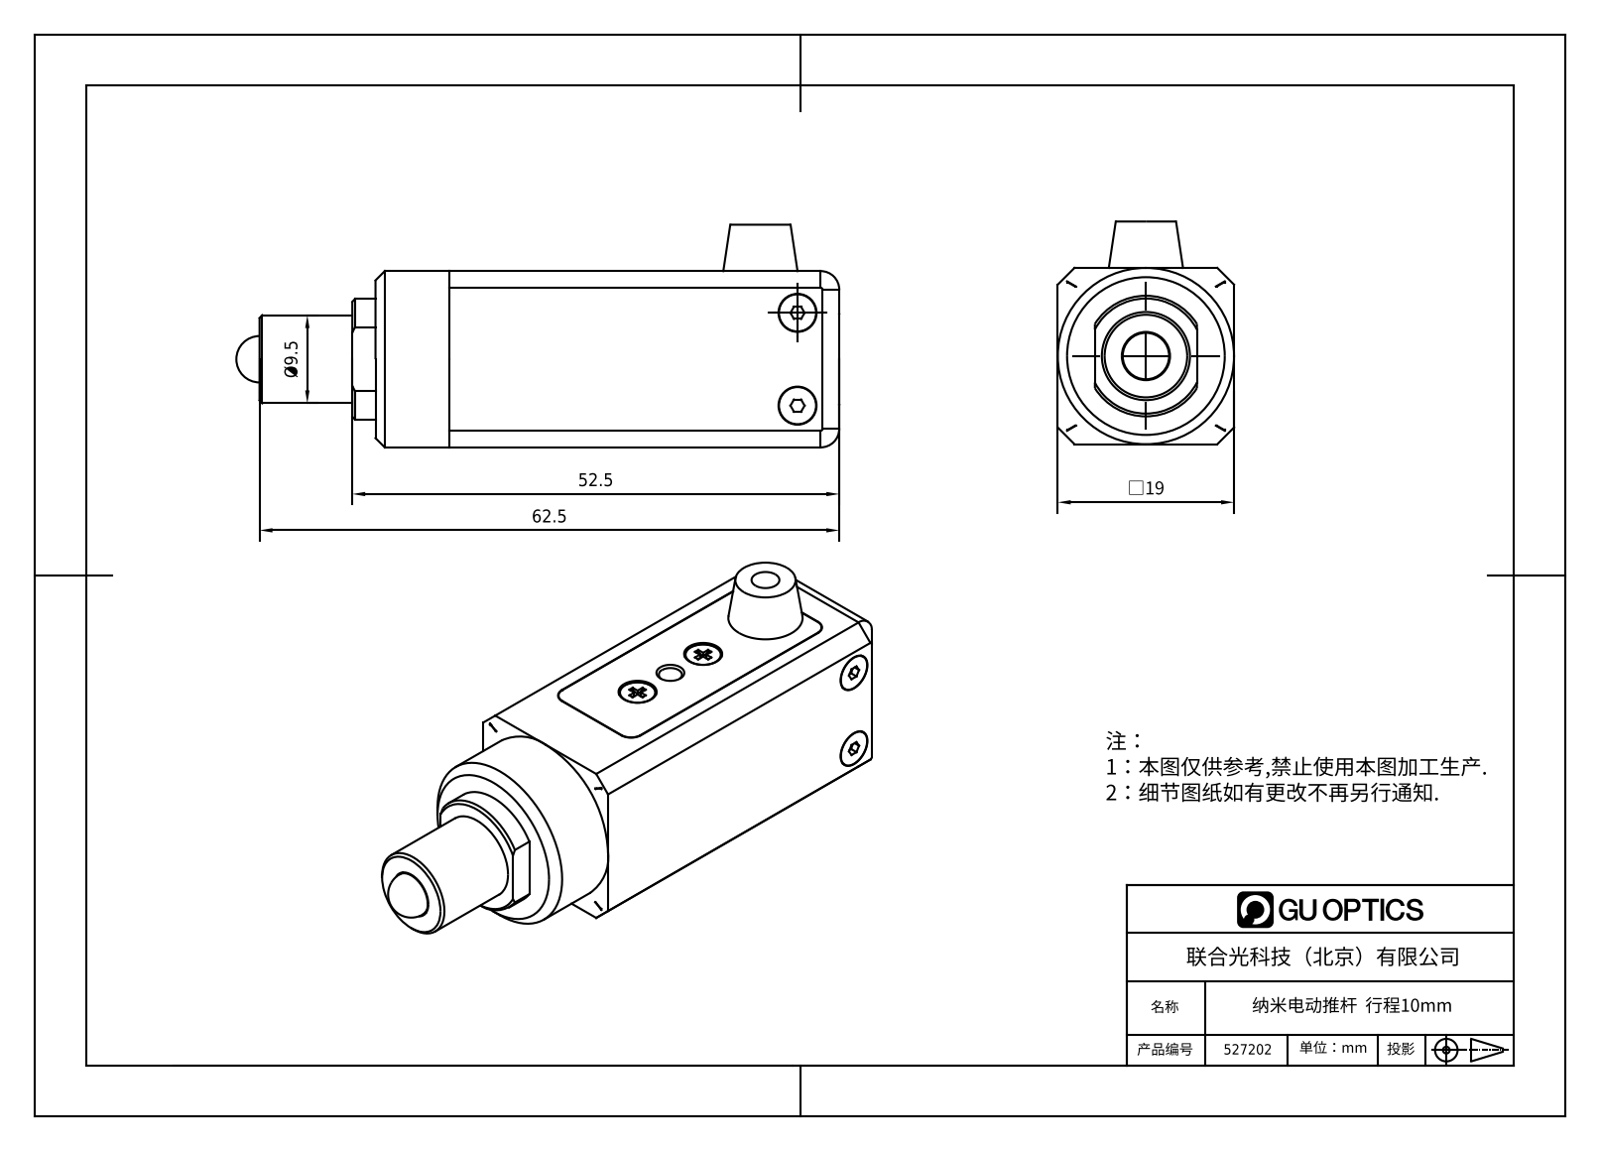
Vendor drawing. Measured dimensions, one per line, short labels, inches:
name: ddtg302_v4_20210828客户
written by: SolidWorks 2021 (AUTOMOTIVE_DESIGN)
unit: in
bodies: 3 solids, 549 faces (302 planar, 178 cylindrical, 69 other)
size: 2.559 × 0.945 × 0.748
volume: 0.974 in³; area: 15.35 in²
holes: 4× ⌀0.087, 4× ⌀0.161, 1× ⌀0.039, 1× ⌀0.083, 1× ⌀0.098, 1× ⌀0.118, 1× ⌀0.197, 1× ⌀0.205, 1× ⌀0.209, 1× ⌀0.238, 1× ⌀0.283, 1× ⌀0.398
bosses: 4× ⌀0.157, 4× ⌀0.079, 1× ⌀0.748, 1× ⌀0.709, 1× ⌀0.394, 1× ⌀0.374, 1× ⌀0.236, 1× ⌀0.197
rounds: 24× R0.059, 4× R0.008, 4× R0.057, 4× R0.118, 2× R0.02, 2× R0.031, 2× R0.039, 2× R0.079
face distances: 0.748, 0.039, 0.071, 0.677, 0.709, 0.031, 0.638, 0.669, 0.026, 0.722
hole spacings: 0.197, 0.394, 0.374, 0.571, 0.735, 0.768, 0.879
